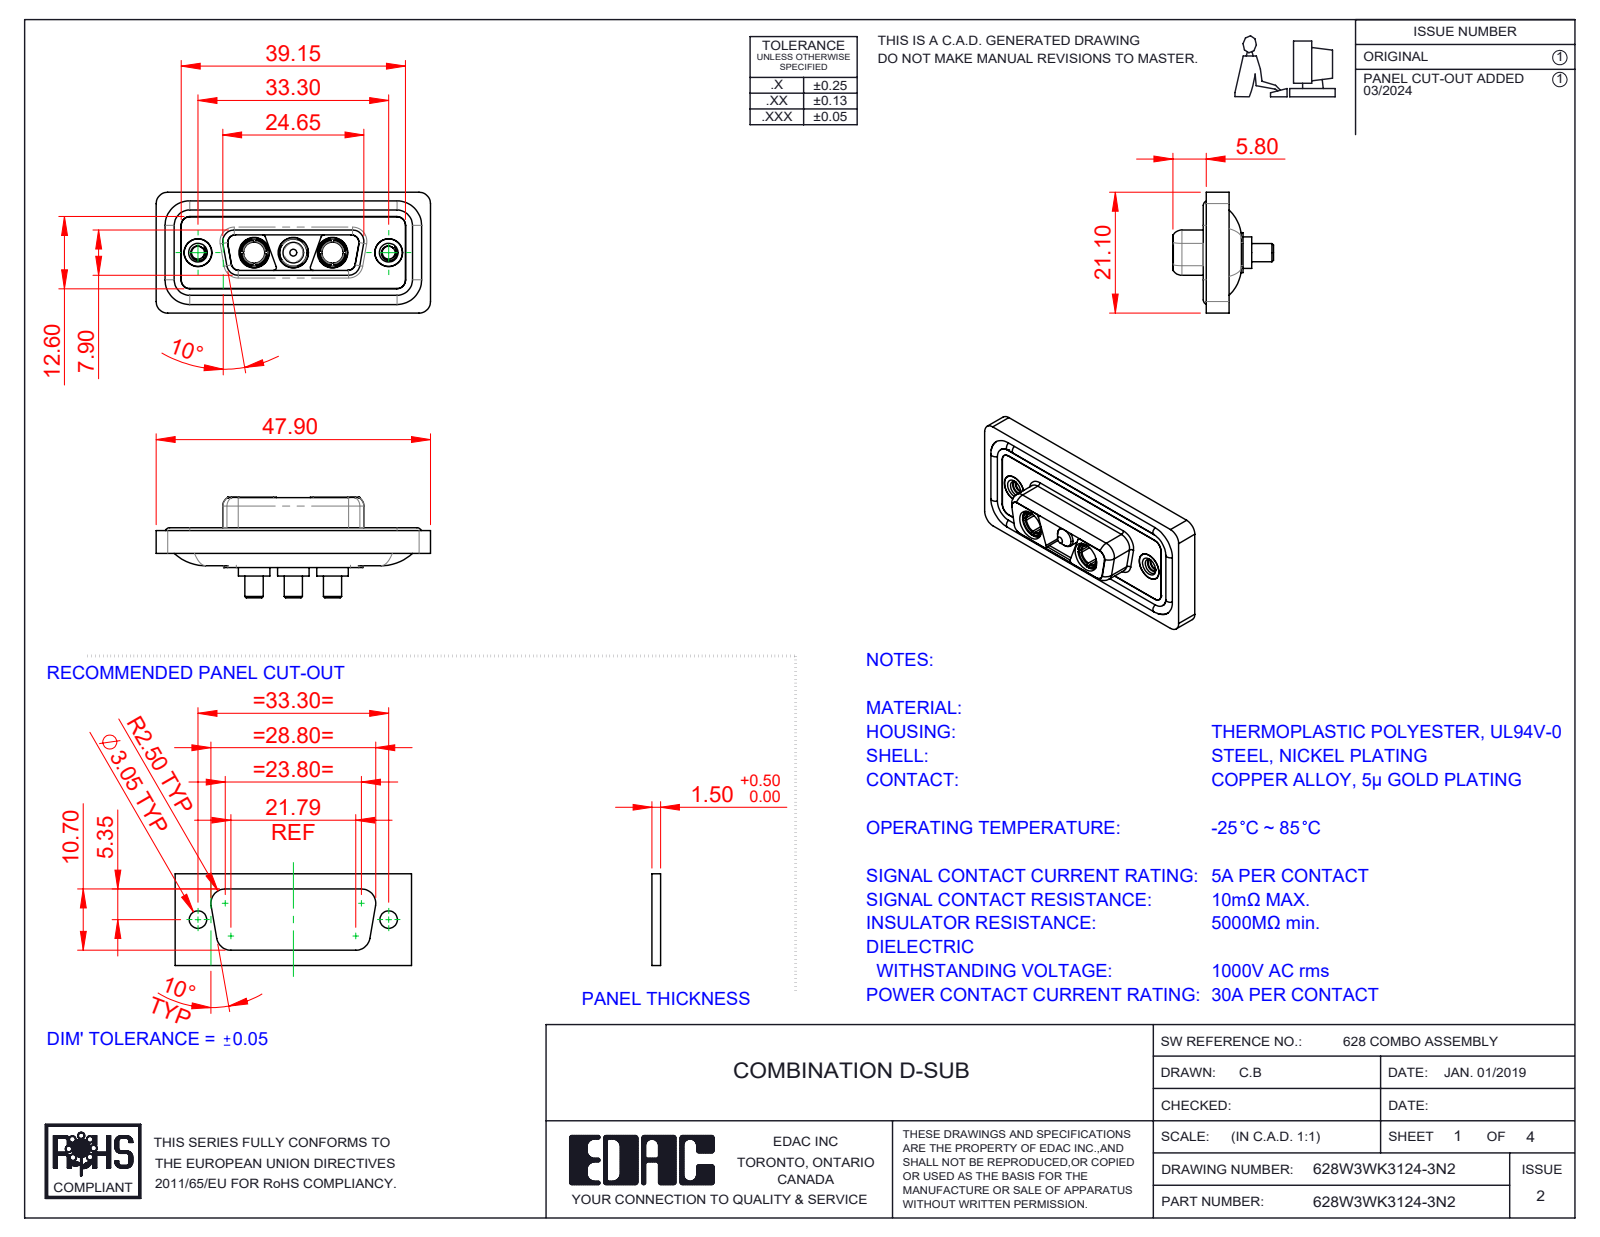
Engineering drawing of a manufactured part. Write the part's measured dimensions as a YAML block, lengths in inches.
part_name: "628Combo Housing_3WK3; Power Socket_30A S; Power Pin_30A S; 628W3WK3124-3N2 (+4 more)"
step_written_by: "SolidWorks 2023 (CONFIG_CONTROL_DESIGN)"
units: inches
bodies: {solids: 13, faces: 583, planar: 178, cylindrical: 258, other: 147}
overall_size: [1.886, 0.831, 0.691]
volume: 0.36
surface_area: 14.75
round_holes:
  - {diameter: 0.191, count: 5}
  - {diameter: 0.209, count: 3}
  - {diameter: 0.089, count: 2}
  - {diameter: 0.146, count: 2}
  - {diameter: 0.157, count: 2}
  - {diameter: 0.159, count: 2}
  - {diameter: 0.197, count: 2}
round_bosses_or_shafts:
  - {diameter: 0.063, count: 4}
  - {diameter: 0.217, count: 3}
  - {diameter: 0.205, count: 3}
  - {diameter: 0.187, count: 3}
  - {diameter: 0.148, count: 3}
  - {diameter: 0.126, count: 3}
  - {diameter: 0.195, count: 2}
  - {diameter: 0.195, count: 2}
partial_cylinders:
  - {radius: 0.059, count: 22}
  - {radius: 0.079, count: 20}
  - {radius: 0.053, count: 12}
  - {radius: 0.02, count: 8}
  - {radius: 0.063, count: 8}
  - {radius: 0.01, count: 4}
  - {radius: 0.024, count: 4}
  - {radius: 0.026, count: 4}
face_to_face_distances: [0.016, 0.063, 0.02, 0.071, 0.043, 0.114, 0.222, 0.278, 0.211, 0.059]
hole_center_spacings: [0.27, 0.386, 0.656, 0.925, 0.539, 1.311]
